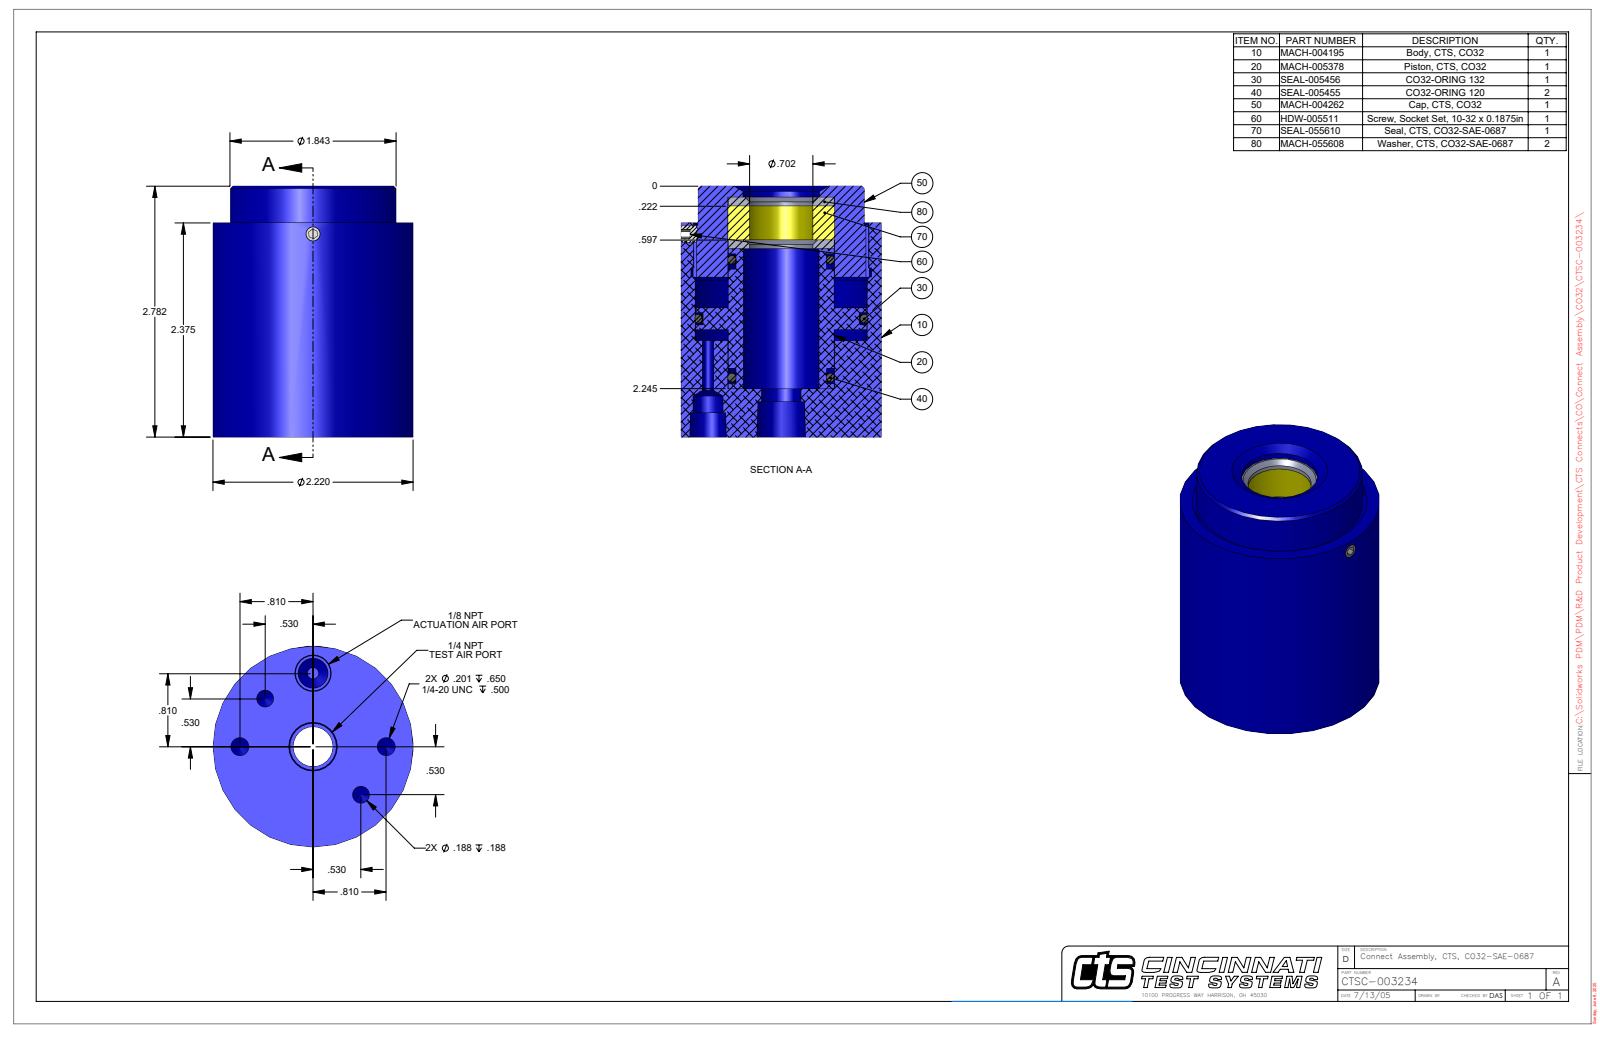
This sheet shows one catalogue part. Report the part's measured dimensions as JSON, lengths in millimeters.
{"part_name": "CTSC-003234", "step_written_by": "SolidWorks 2023 (AUTOMOTIVE_DESIGN)", "units": "millimeters", "bodies": {"solids": 1, "faces": 118, "planar": 49, "cylindrical": 44, "other": 25}, "overall_size": [70.7, 56.4, 56.4], "volume_mm3": 145800, "surface_area_mm2": 22920, "round_holes": [[4.7, 2], [5.1, 2], [2.4, 1], [3.2, 1], [4, 1], [8.4, 1], [11.1, 1], [17.8, 1], [21.3, 1], [21.5, 1], [30, 1], [49.4, 1]], "round_bosses_or_shafts": [[56.4, 1], [46.8, 1], [29.8, 1]], "partial_cylinders_radius": [[2.4, 1], [27.8, 1]], "face_to_face_distances": [70.7, 60.3, 10.3, 13.6, 46.7, 57, 59.6, 45.9, 0.8, 11.1], "hole_center_spacings": [15.2, 20.6, 36.6, 19.1, 29.1, 38.1, 41.1]}
